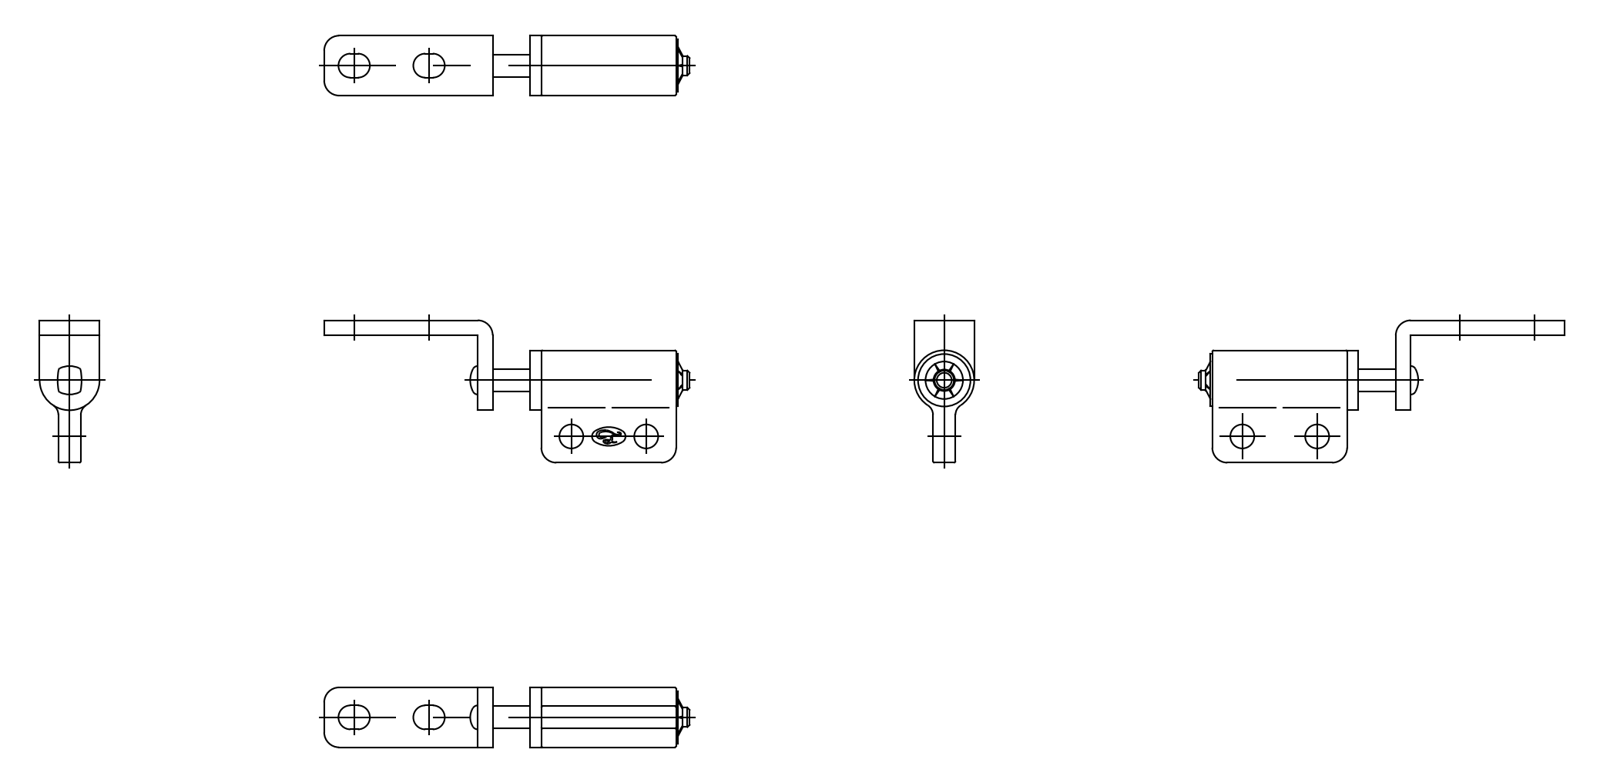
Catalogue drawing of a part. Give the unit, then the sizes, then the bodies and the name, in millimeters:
Units: millimetres
Overall size (bounding box): 48.8 × 19 × 8
Round holes (diameter × count): ⌀3.2 ×2, ⌀3 ×1, ⌀6 ×1
Round bosses / shafts (diameter × count): ⌀8 ×1, ⌀7 ×1, ⌀5.7 ×1, ⌀3 ×1, ⌀2.6 ×1
Partial cylindrical surfaces — rounded edges, fillets, slot ends (radius × count): R1 ×9, R0.2 ×6, R1.6 ×4, R2 ×4, R0.28 ×2, R0.56 ×2, R0.78 ×2, R0.83 ×2
Main face-to-face distances: 2, 1.25, 5.5, 2.5, 3, 6.75, 4.25, 8, 5, 7
Hole centre spacings: 5.02, 10
Volume: 1 778 mm³ · Surface area: 2 036 mm²
Bodies: 1 solid, 171 faces (51 planar, 88 cylindrical, 32 other)
STEP written by: spGate 18.9.1 (****-****-****-****) (AUTOMOTIVE_DESIGN)
